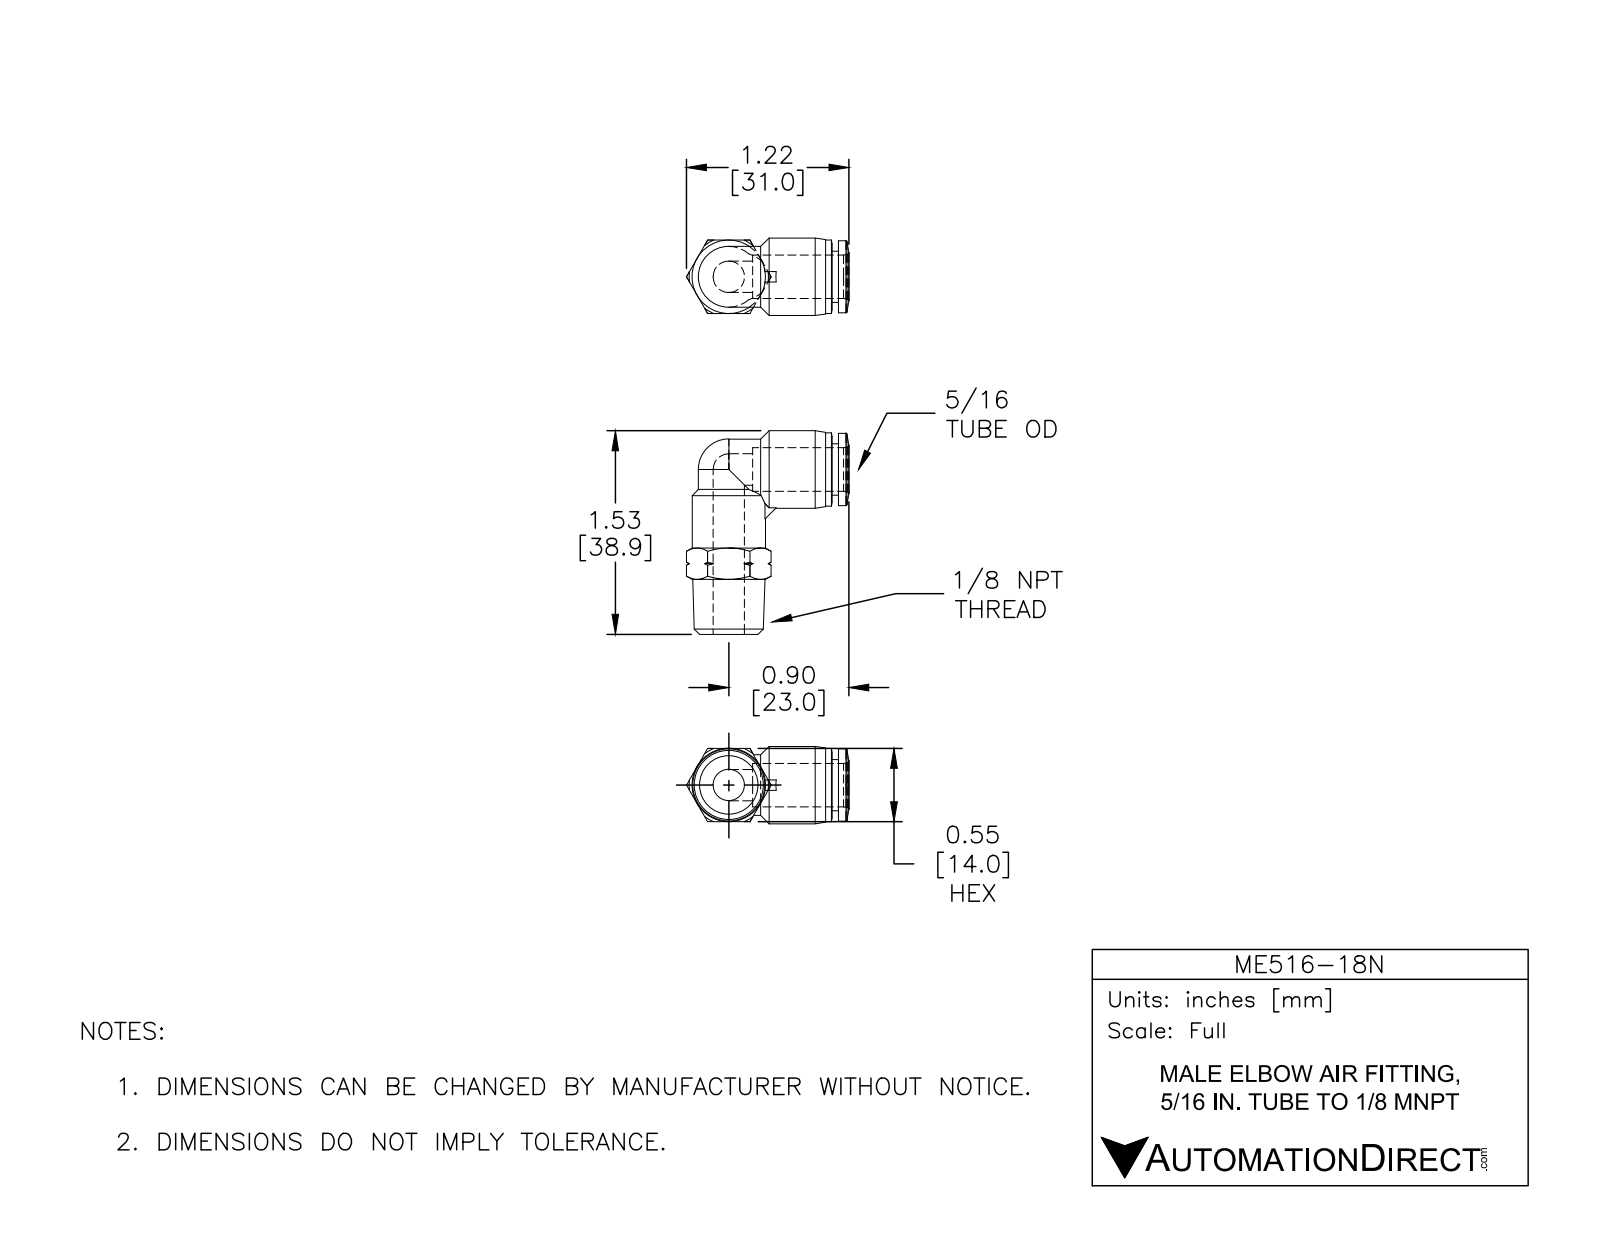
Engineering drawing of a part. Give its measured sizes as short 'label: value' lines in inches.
name: ME516-18N
written by: SolidWorks 2015 (CONFIG_CONTROL_DESIGN)
unit: in
bodies: 1 solid, 88 faces (15 planar, 21 cylindrical, 52 other)
size: 1.453 × 1.222 × 0.583
volume: 0.307 in³; area: 5.639 in²
holes: 2× ⌀0.236, 1× ⌀0.327
bosses: 2× ⌀0.551, 1× ⌀0.583, 1× ⌀0.543, 1× ⌀0.457, 1× ⌀0.386
rounds: 1× R0.228
face distances: 0.551, 0.047, 0.335, 0.598, 0.646, 0.236, 0.315, 0.549, 0.049, 0.096
